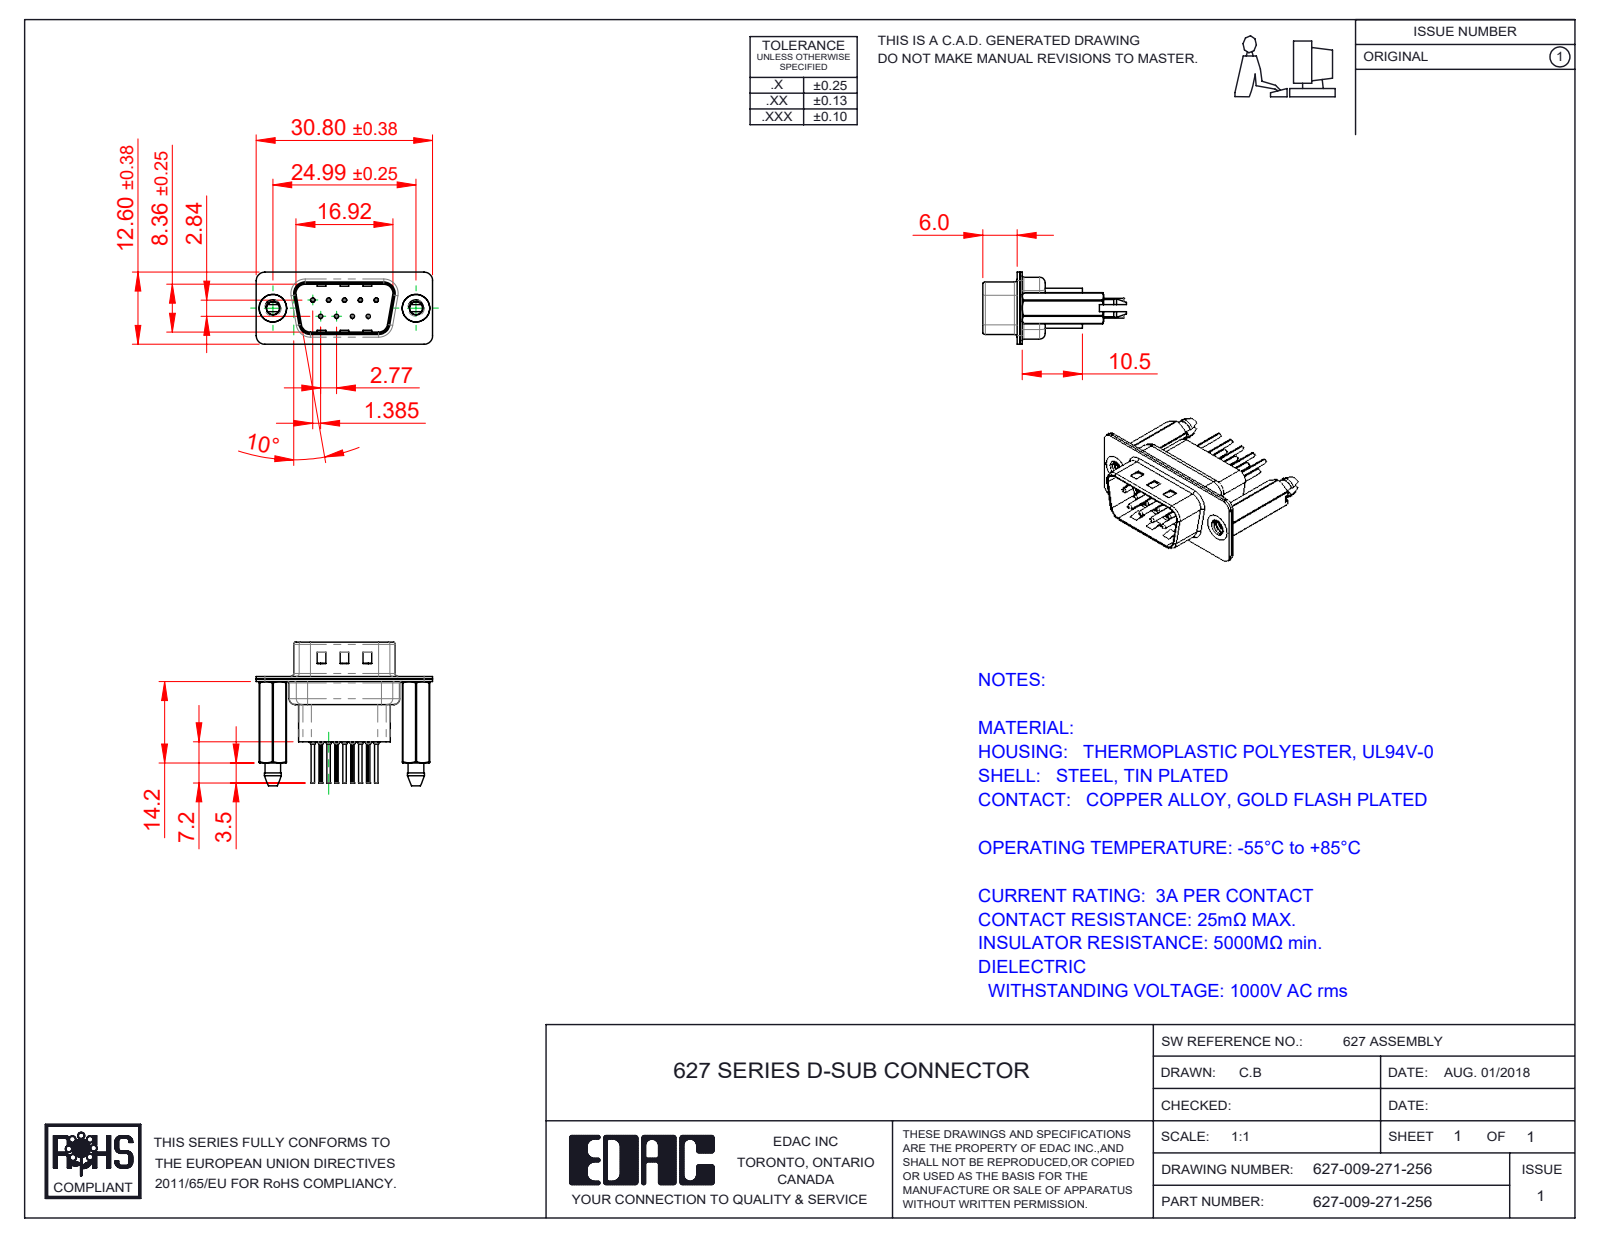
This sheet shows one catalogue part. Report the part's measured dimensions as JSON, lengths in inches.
{"part_name": "627 Housing_09 HP; 627 Contact Row 2_61; 627 4-40 Threaded Boardlock_HP71; 627-009-271-256 (+3 more)", "step_written_by": "SolidWorks 2020 (CONFIG_CONTROL_DESIGN)", "units": "inches", "bodies": {"solids": 14, "faces": 1294, "planar": 355, "cylindrical": 528, "other": 411}, "overall_size": [1.213, 0.988, 0.496], "volume_in3": 0.13, "surface_area_in2": 8.587, "round_holes": [[0.008, 9], [0.014, 9], [0.043, 9], [0.063, 9], [0.089, 2], [0.157, 2], [0.189, 2]], "round_bosses_or_shafts": [[0.079, 9], [0.059, 9], [0.03, 9], [0.024, 9], [0.193, 2]], "partial_cylinders_radius": [[0.059, 20], [0.004, 18], [0.079, 12], [0.063, 10], [0.02, 8], [0.01, 4], [0.024, 4], [0.026, 4]], "face_to_face_distances": [0.018, 0.016, 0.035, 0.032, 0.377, 0.055, 0.187, 0.059, 0.027, 0.302], "hole_center_spacings": [0.124, 0.109, 0.218, 0.198, 0.198, 0.327, 0.294, 0.295]}
